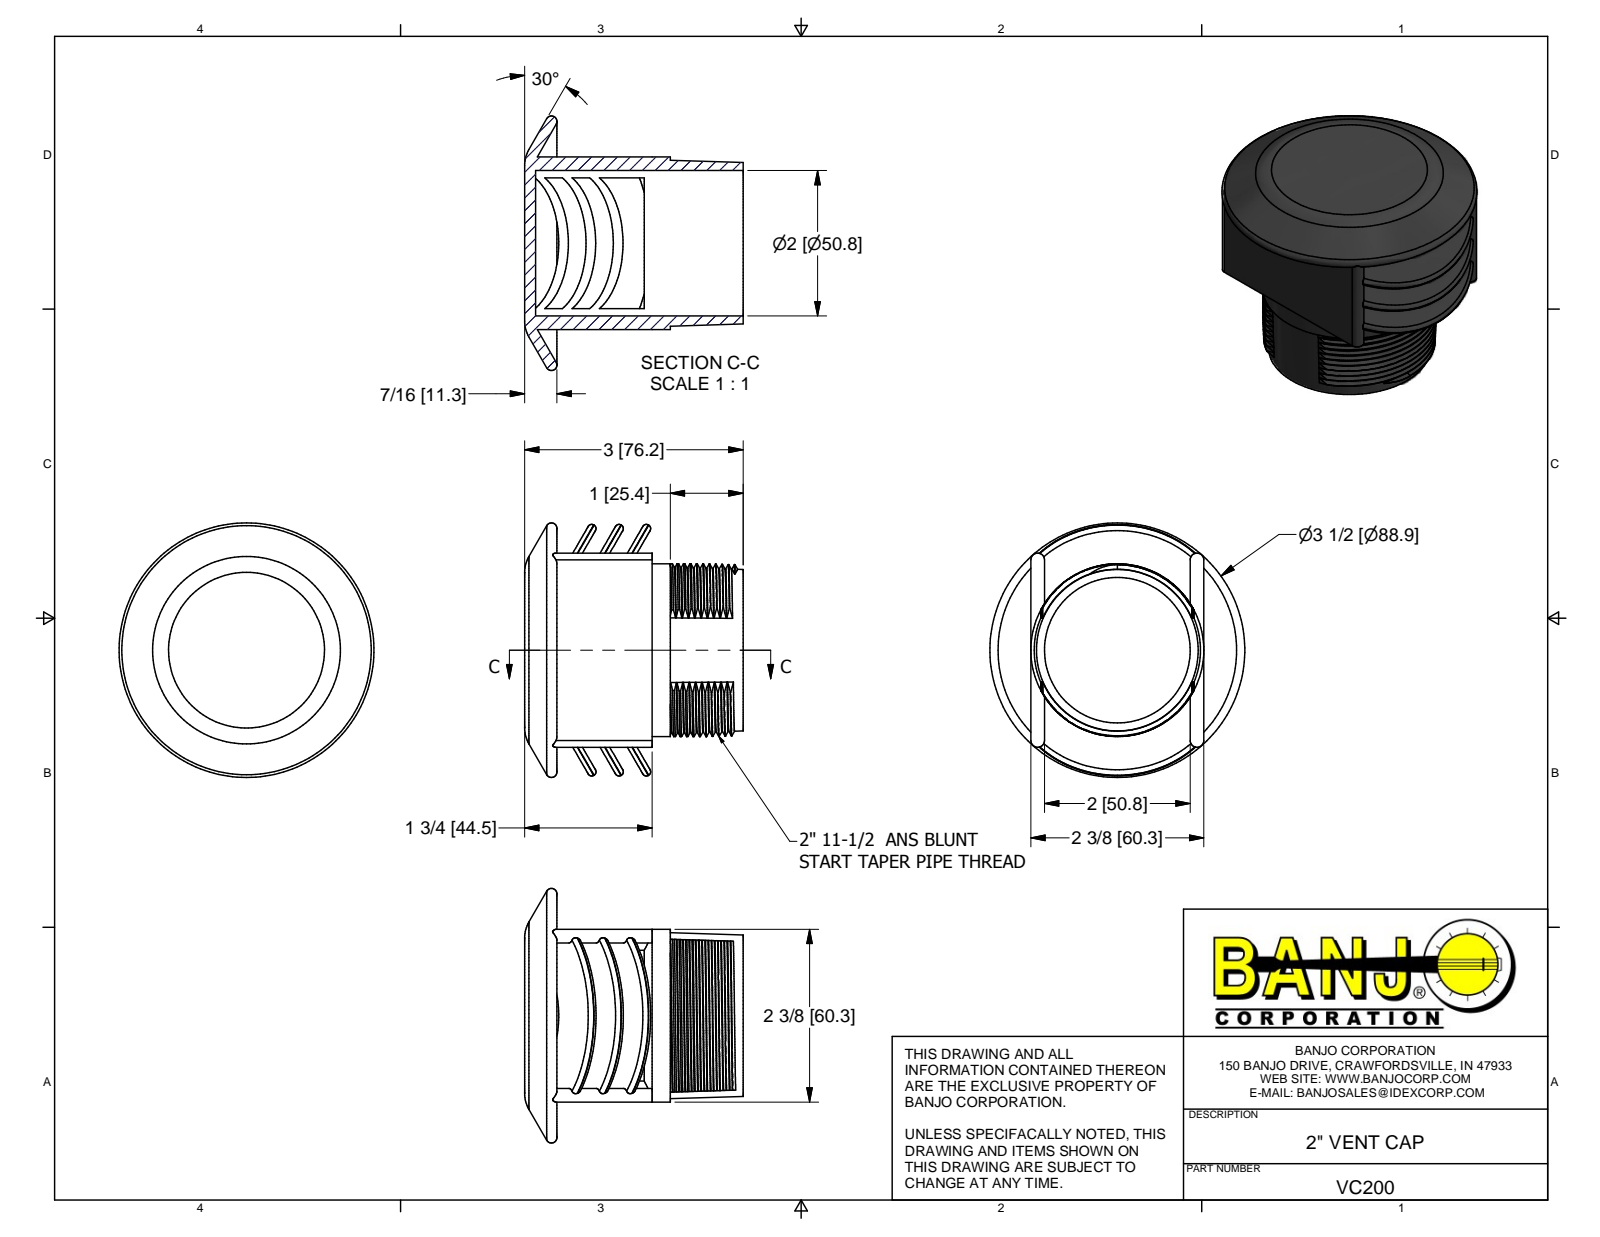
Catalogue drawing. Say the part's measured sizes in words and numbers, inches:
The part is named "VC200". Its 3-D file was written by "Autodesk Inventor 2016 (AUTOMOTIVE_DESIGN)". It is 1 solid with 193 faces: 92 planar, 24 cylindrical and 77 other. Overall it measures 3.5 by 3.5 by 3 inches. Its volume is 5.715 cubic inches and its surface area 84.95 square inches. Round holes: 1 of diameter 2. Round bosses or shafts: 1 of diameter 2.375. Partial cylindrical surfaces (rounded edges, fillets, slot ends): 6 of radius 1.488, 4 of radius 0.094, 1 of radius 0.619. The main face-to-face distances are 0.325, 0.115, 0.65, 0.44, 0.21, 2.375, 0.15, 0.187, 2.187, 0.765.
